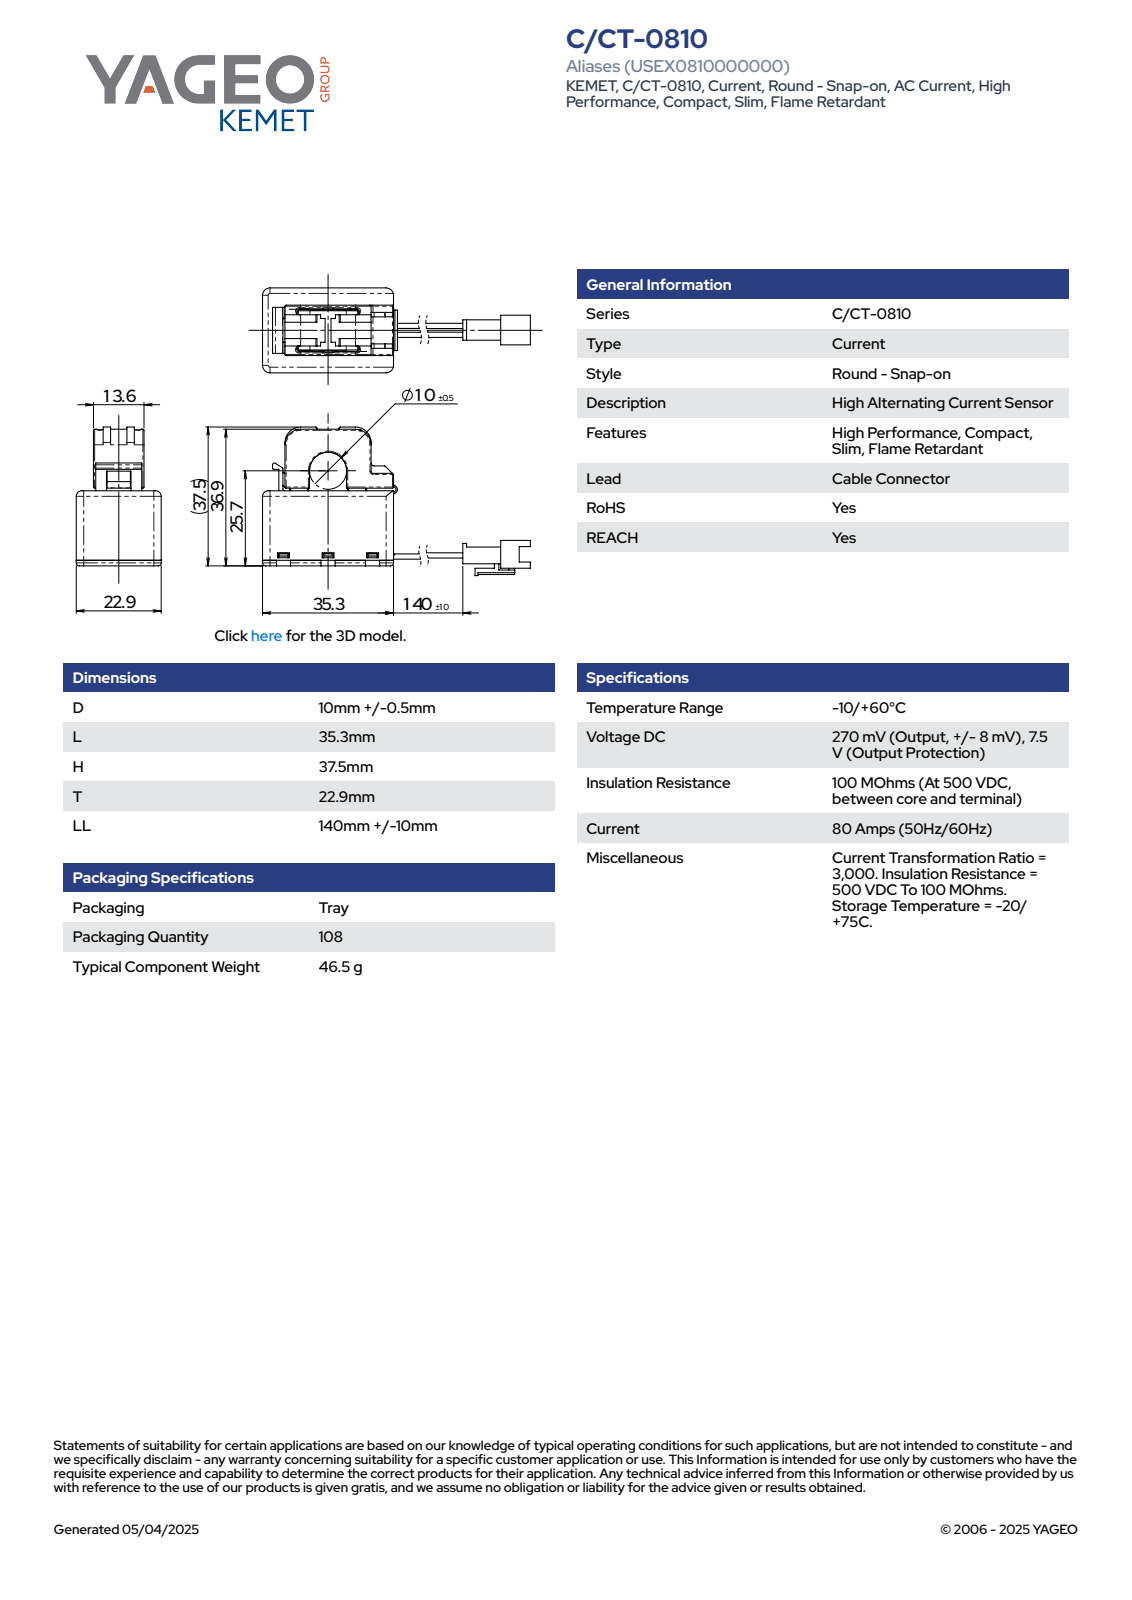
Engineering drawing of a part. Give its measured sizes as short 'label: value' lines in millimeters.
name: CCT-0810(AP214)
written by: SolidWorks 2021 (AUTOMOTIVE_DESIGN)
unit: mm
bodies: 1 solid, 279 faces (186 planar, 71 cylindrical, 22 other)
size: 193.3 × 40.2 × 22.9
volume: 21 645 mm³; area: 7 972 mm²
bosses: 2× ⌀1.4
rounds: 20× R0.6, 14× R0.3, 5× R0.8, 4× R0.5, 4× R2, 4× R4.2, 3× R1.5, 1× R0.47
face distances: 18.25, 22.9, 4.65, 20.25, 35.3, 13.6, 1.25, 16.6, 6.05, 29.25
